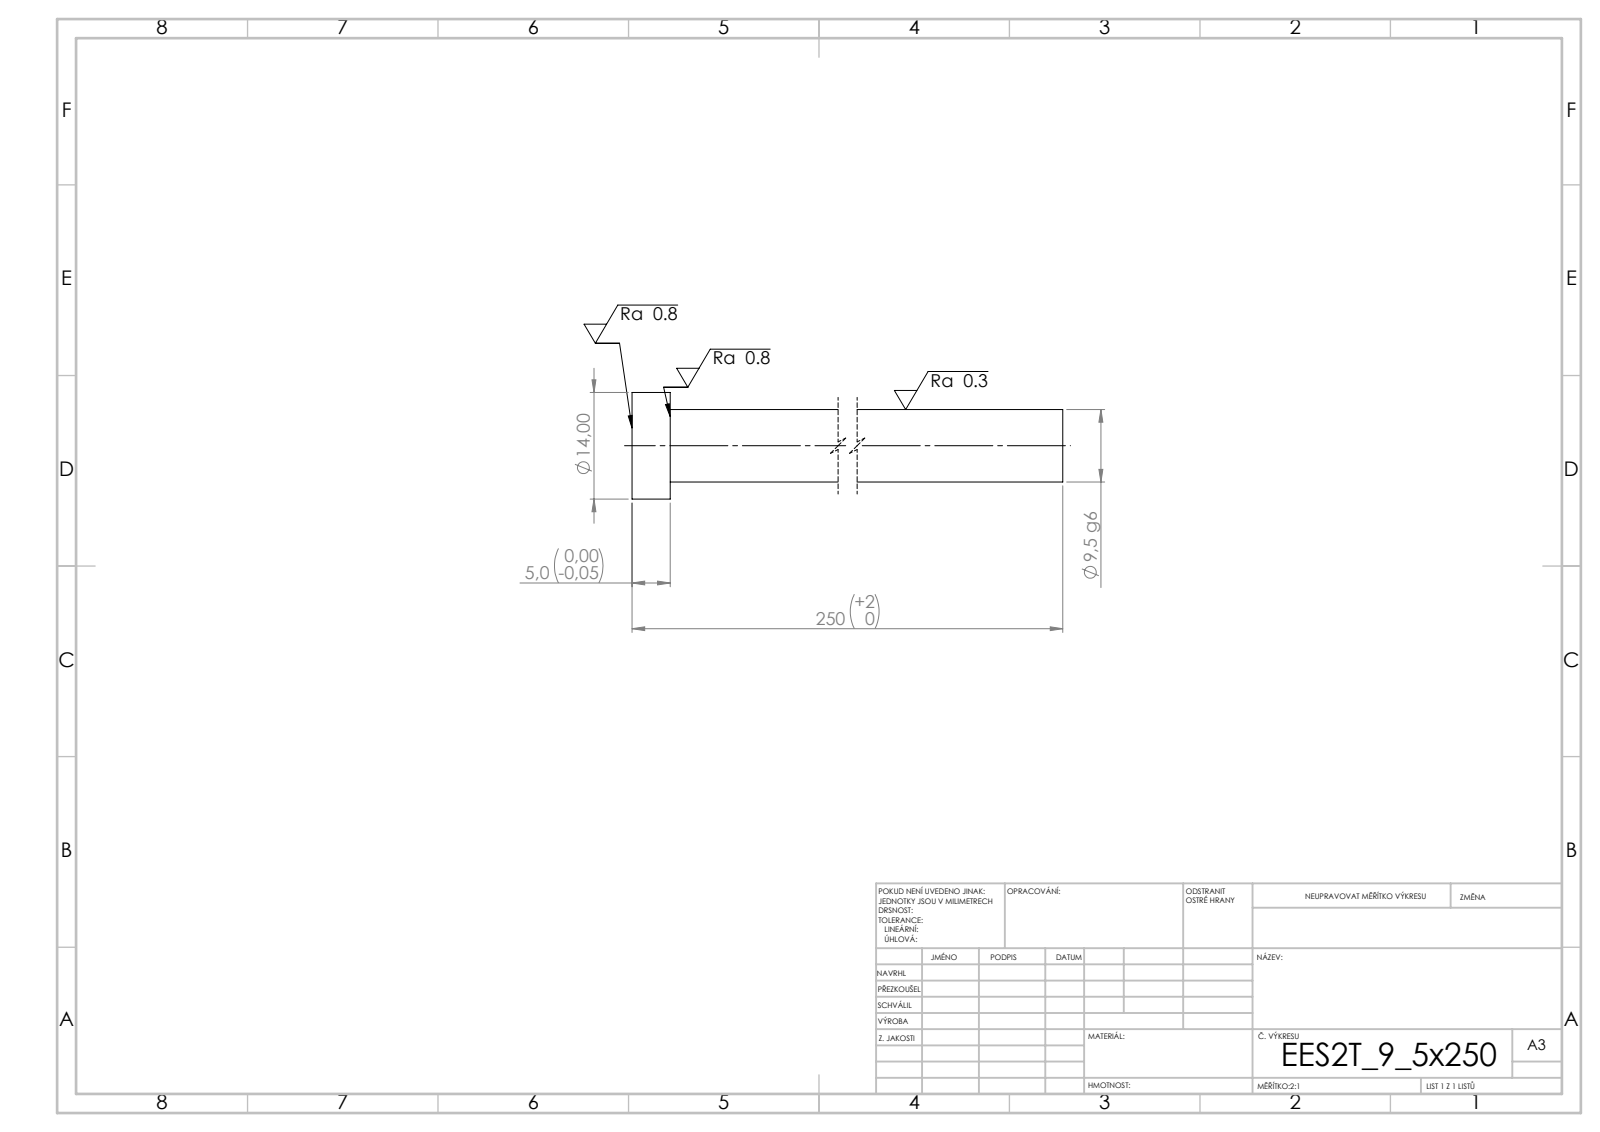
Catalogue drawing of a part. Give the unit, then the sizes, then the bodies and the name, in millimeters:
Units: millimetres
Overall size (bounding box): 250 × 14 × 14
Round bosses / shafts (diameter × count): ⌀14 ×1, ⌀9.5 ×1
Main face-to-face distances: 5, 250, 245
Volume: 18 136 mm³ · Surface area: 7 840 mm²
Bodies: 1 solid, 7 faces (3 planar, 4 cylindrical, 0 other)
STEP written by: SolidWorks 2019 (CONFIG_CONTROL_DESIGN)
